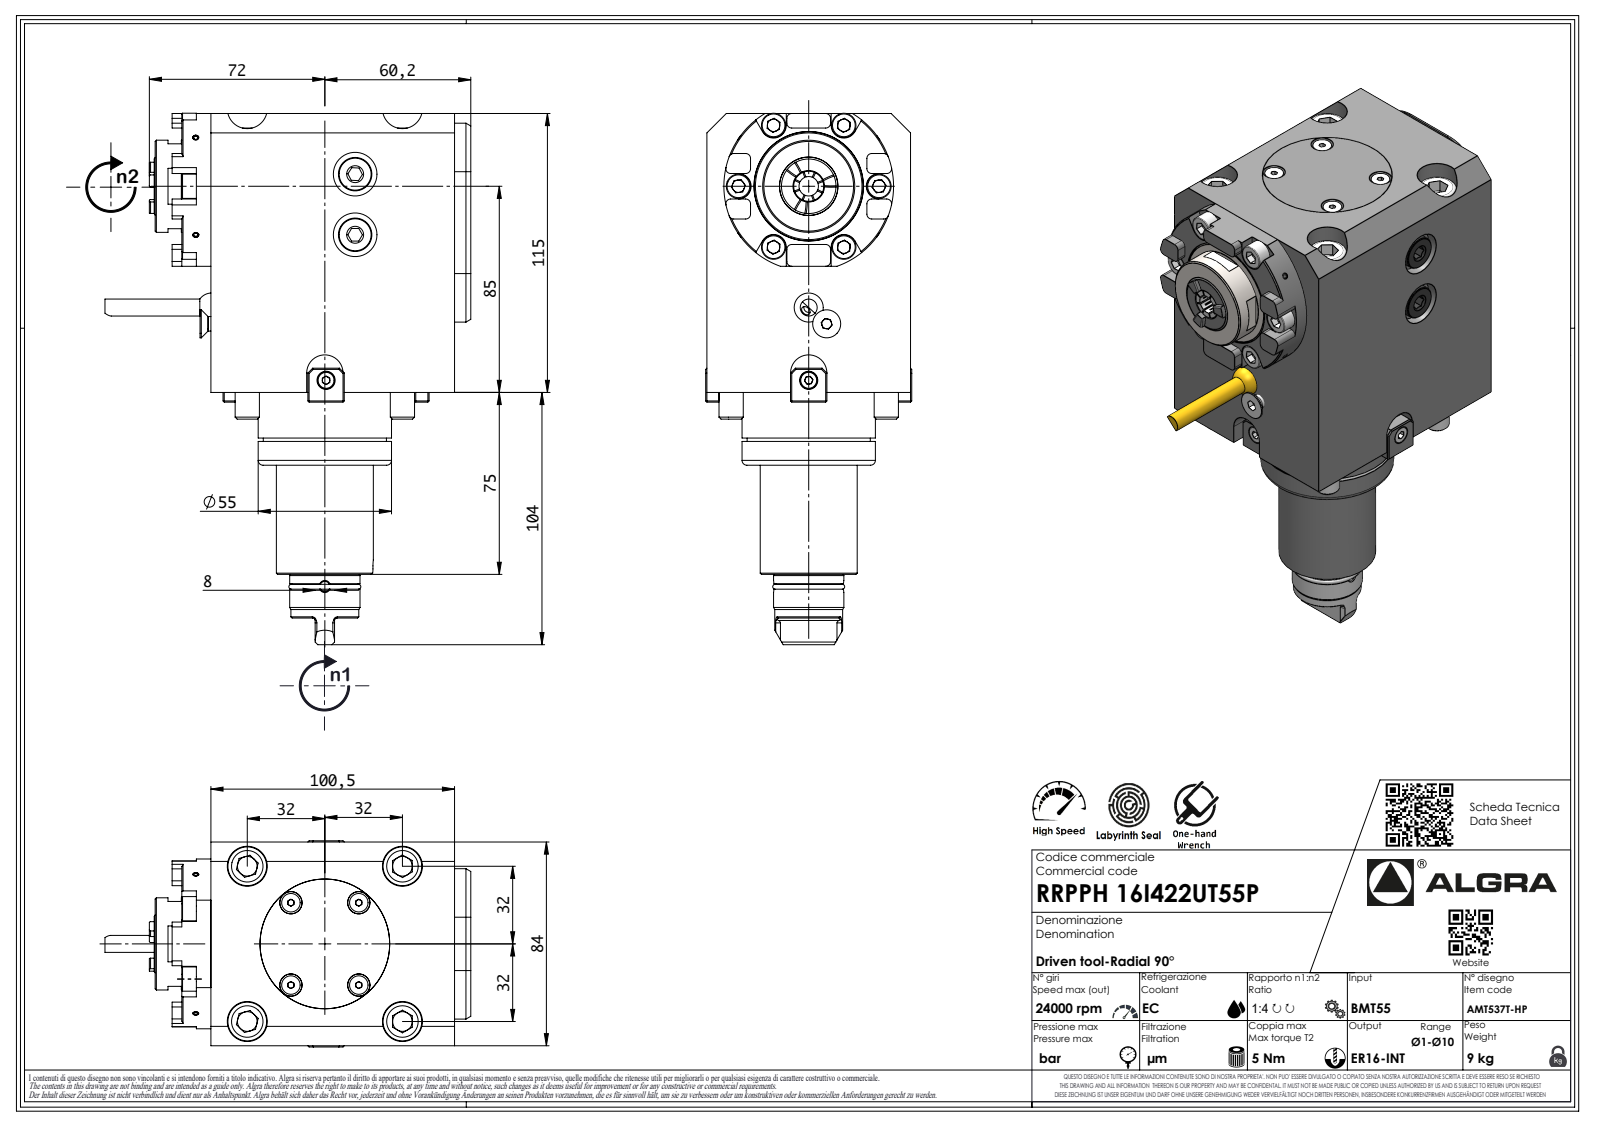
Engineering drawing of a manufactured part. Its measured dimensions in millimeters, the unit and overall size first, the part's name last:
Units: millimetres
Overall size (bounding box): 219 × 130.2 × 84
Round holes (diameter × count): ⌀2.1 ×1
Round bosses / shafts (diameter × count): ⌀10 ×3, ⌀55 ×1, ⌀50.8 ×1, ⌀40 ×1, ⌀38 ×1, ⌀29 ×1, ⌀28 ×1, ⌀6.37 ×1
Partial cylindrical surfaces — rounded edges, fillets, slot ends (radius × count): R2 ×28, R0.33 ×7, R0.52 ×7, R3.7 ×7, R5.25 ×6, R20 ×4, R1 ×2, R2.25 ×2
Main face-to-face distances: 84, 115, 100.5, 107.2, 6.7, 11, 6, 12, 112.5, 119.2
Volume: 1 195 000 mm³ · Surface area: 80 541 mm²
Bodies: 1 solid, 570 faces (379 planar, 83 cylindrical, 108 other)
Part name (STEP PRODUCT): RRPPH16I422UT55P
STEP written by: SolidWorks 2023 (AUTOMOTIVE_DESIGN)
